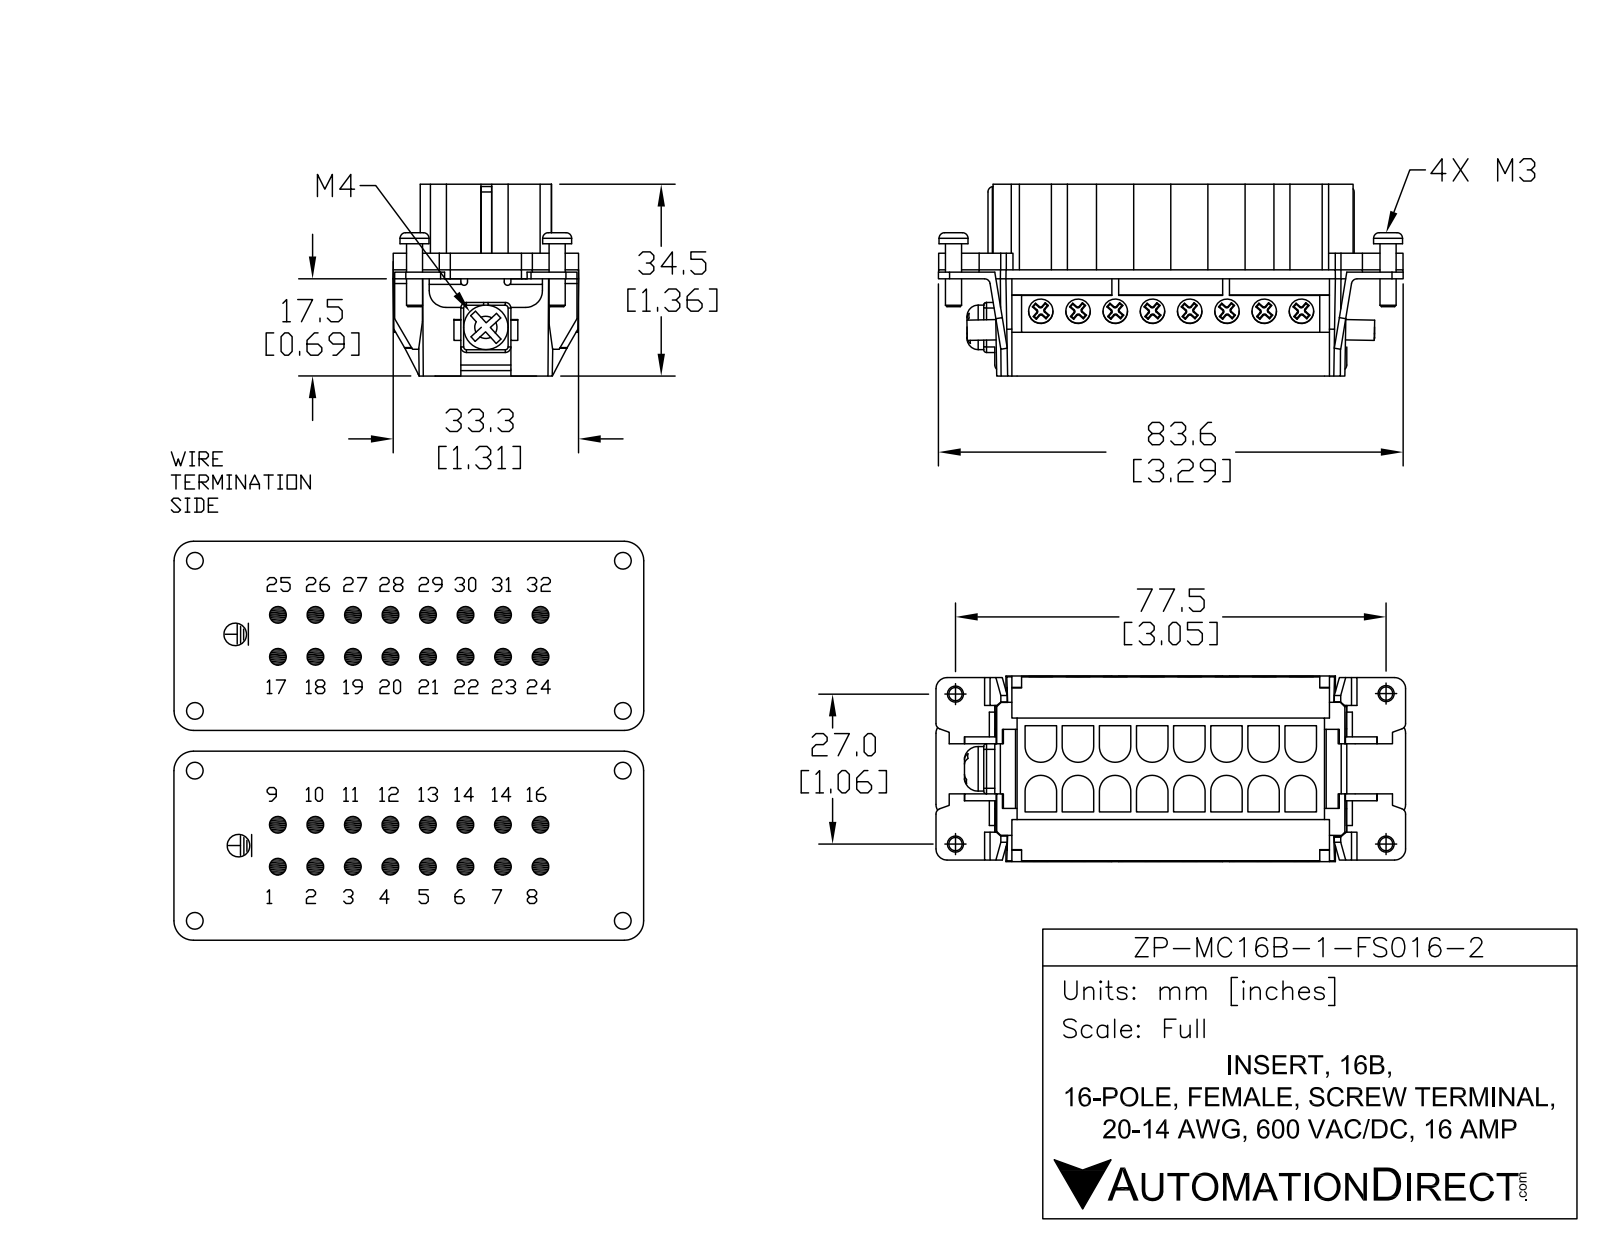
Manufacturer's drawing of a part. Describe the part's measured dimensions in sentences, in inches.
The part is named "ZP-MC16B-1-FS016-2". Its 3-D file was written by "SolidWorks 2021 (CONFIG_CONTROL_DESIGN)". It is 1 solid with 2048 faces: 1172 planar, 425 cylindrical and 451 other. Overall it measures 3.346 by 1.378 by 1.331 inches. Its volume is 2.626 cubic inches and its surface area 34.32 square inches. Round holes: 12 of diameter 0.226, 7 of diameter 0.071, 4 of diameter 0.106. Round bosses or shafts: 4 of diameter 0.213, 4 of diameter 0.205, 4 of diameter 0.118, 4 of diameter 0.091, 1 of diameter 0.276, 1 of diameter 0.197, 1 of diameter 0.157, 1 of diameter 0.142. Partial cylindrical surfaces (rounded edges, fillets, slot ends): 70 of radius 0.008, 32 of radius 0.012, 30 of radius 0.02, 20 of radius 0.039, 14 of radius 0.047, 12 of radius 0.02, 12 of radius 0.024, 10 of radius 0.079. The main face-to-face distances are 0.047, 0.283, 0.108, 0.392, 0.72, 0.61, 1.236, 0.854, 0.736, 0.626. The hole center spacings are 0.198, 0.422, 0.264, 0.676, 0.528, 0.935, 0.396, 0.791.
